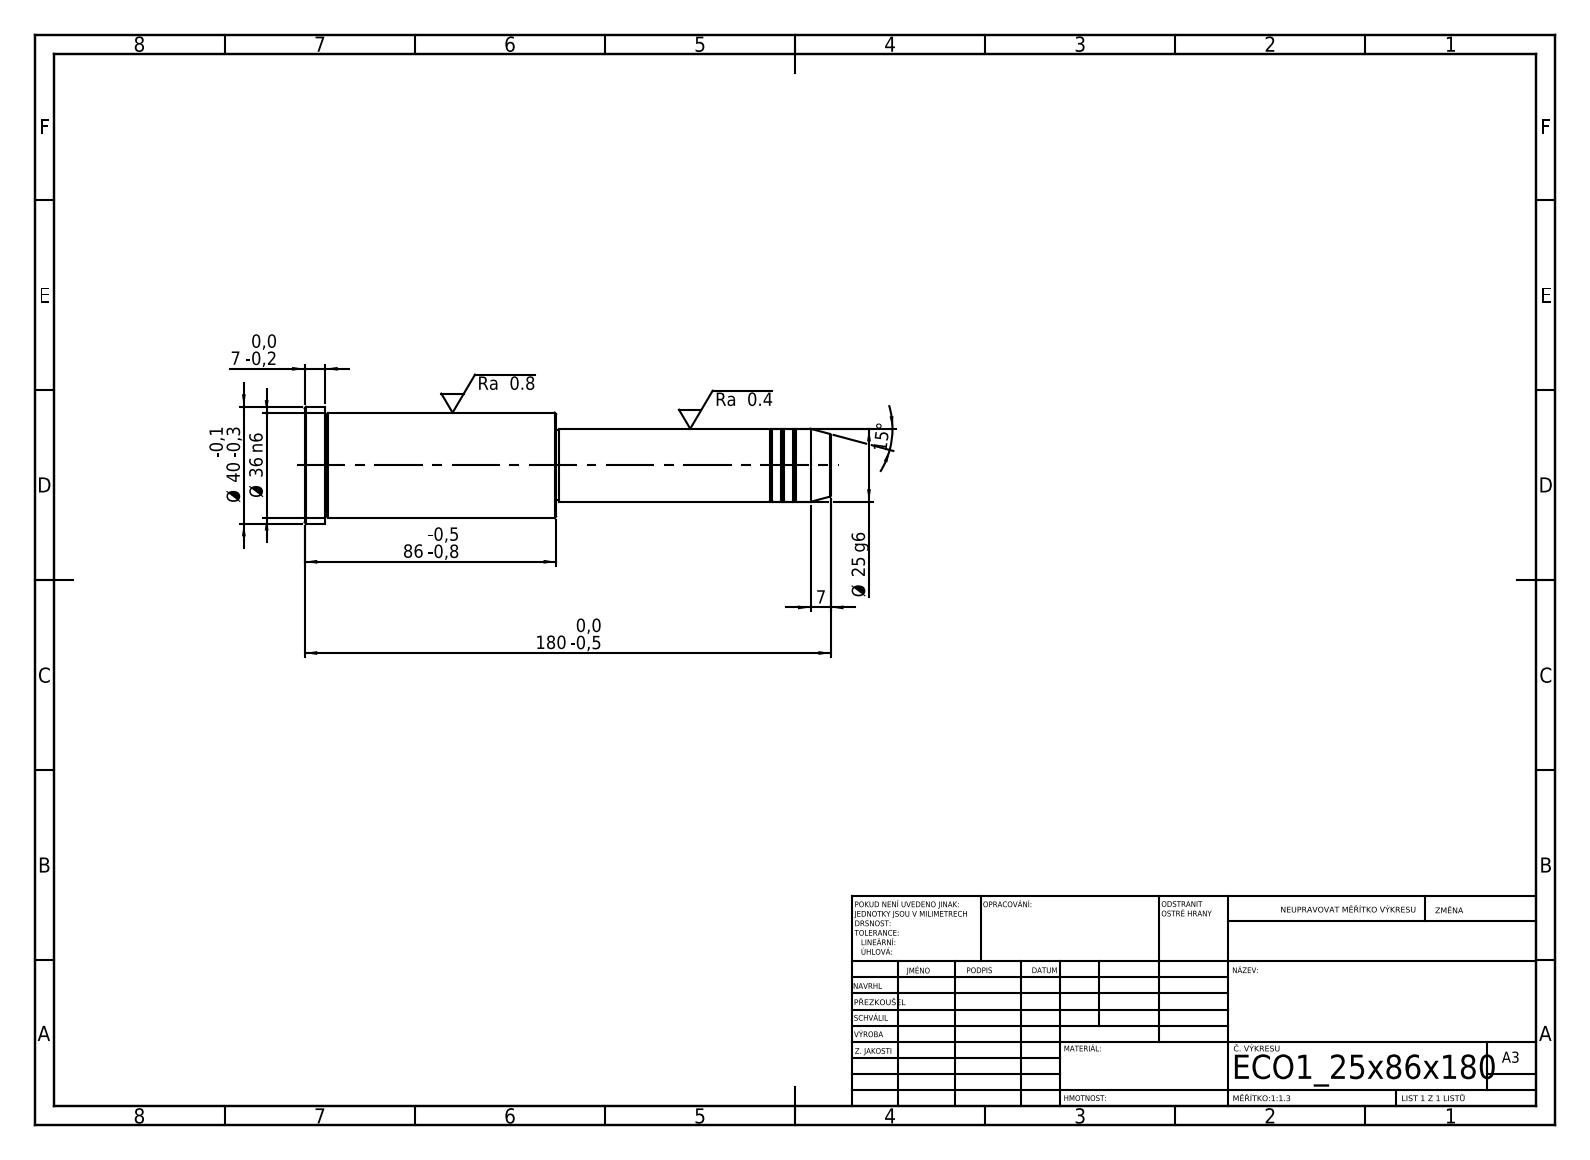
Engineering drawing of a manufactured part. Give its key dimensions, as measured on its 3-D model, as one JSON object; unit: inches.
{"step_written_by": "SolidWorks 2019 (CONFIG_CONTROL_DESIGN)", "units": "inches", "bodies": {"solids": 1, "faces": 43, "planar": 5, "cylindrical": 14, "other": 24}, "overall_size": [7.087, 1.575, 1.575], "volume_in3": 8.217, "surface_area_in2": 30.59, "round_bosses_or_shafts": [[1.575, 1], [1.417, 1], [0.984, 1], [0.945, 1]], "face_to_face_distances": [3.386, 3.701, 7.087, 6.811, 3.11, 0.276, 3.661, 0.039, 3.15, 3.425]}
